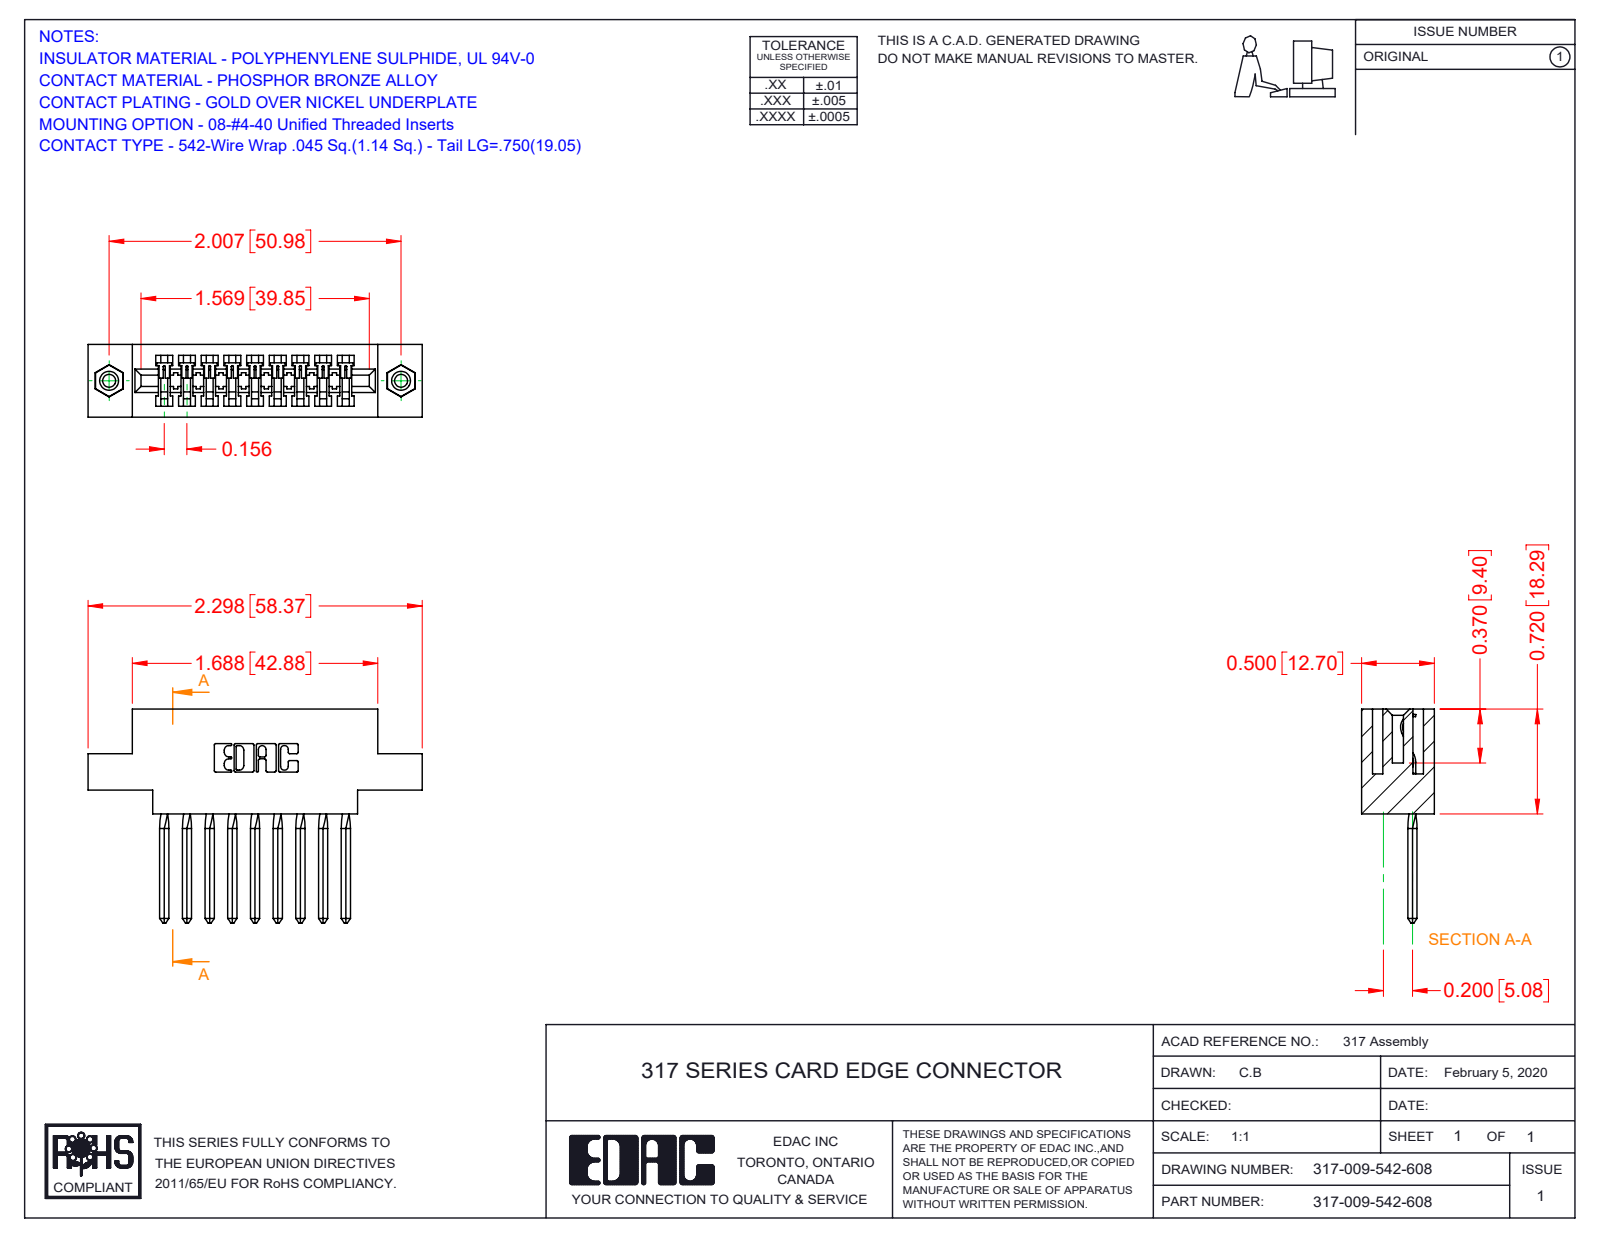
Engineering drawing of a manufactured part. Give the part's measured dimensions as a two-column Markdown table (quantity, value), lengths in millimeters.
| quantity | value |
| --- | --- |
| part name | 345-250-001_345-250-003-102; 317-290-003_542; 317 Part_.156 Dia - TI; 317-009-542-678 |
| STEP written by | SolidWorks 2016 (CONFIG_CONTROL_DESIGN) |
| units | millimeters |
| bodies | 12 solids, 837 faces (666 planar, 119 cylindrical, 52 other) |
| overall size | 58.4 × 37.3 × 12.7 |
| volume | 8 130 mm³ |
| surface area | 9 206 mm² |
| round holes (diameter × count) | 2.3 × 2, 3.2 × 2, 4 × 2 |
| round bosses / shafts (diameter × count) | 3.9 × 2 |
| partial cylindrical surfaces (radius × count) | 0.3 × 22, 0.2 × 18, 0.2 × 6, 0.8 × 6, 0.7 × 3, 1.9 × 1, 2.3 × 1, 2.5 × 1 |
| main face-to-face distances | 12.7, 1.9, 10.8, 2.8, 1.7, 5.6, 4, 8.9, 2.9, 3.5 |
| hole center spacings | 51 |
